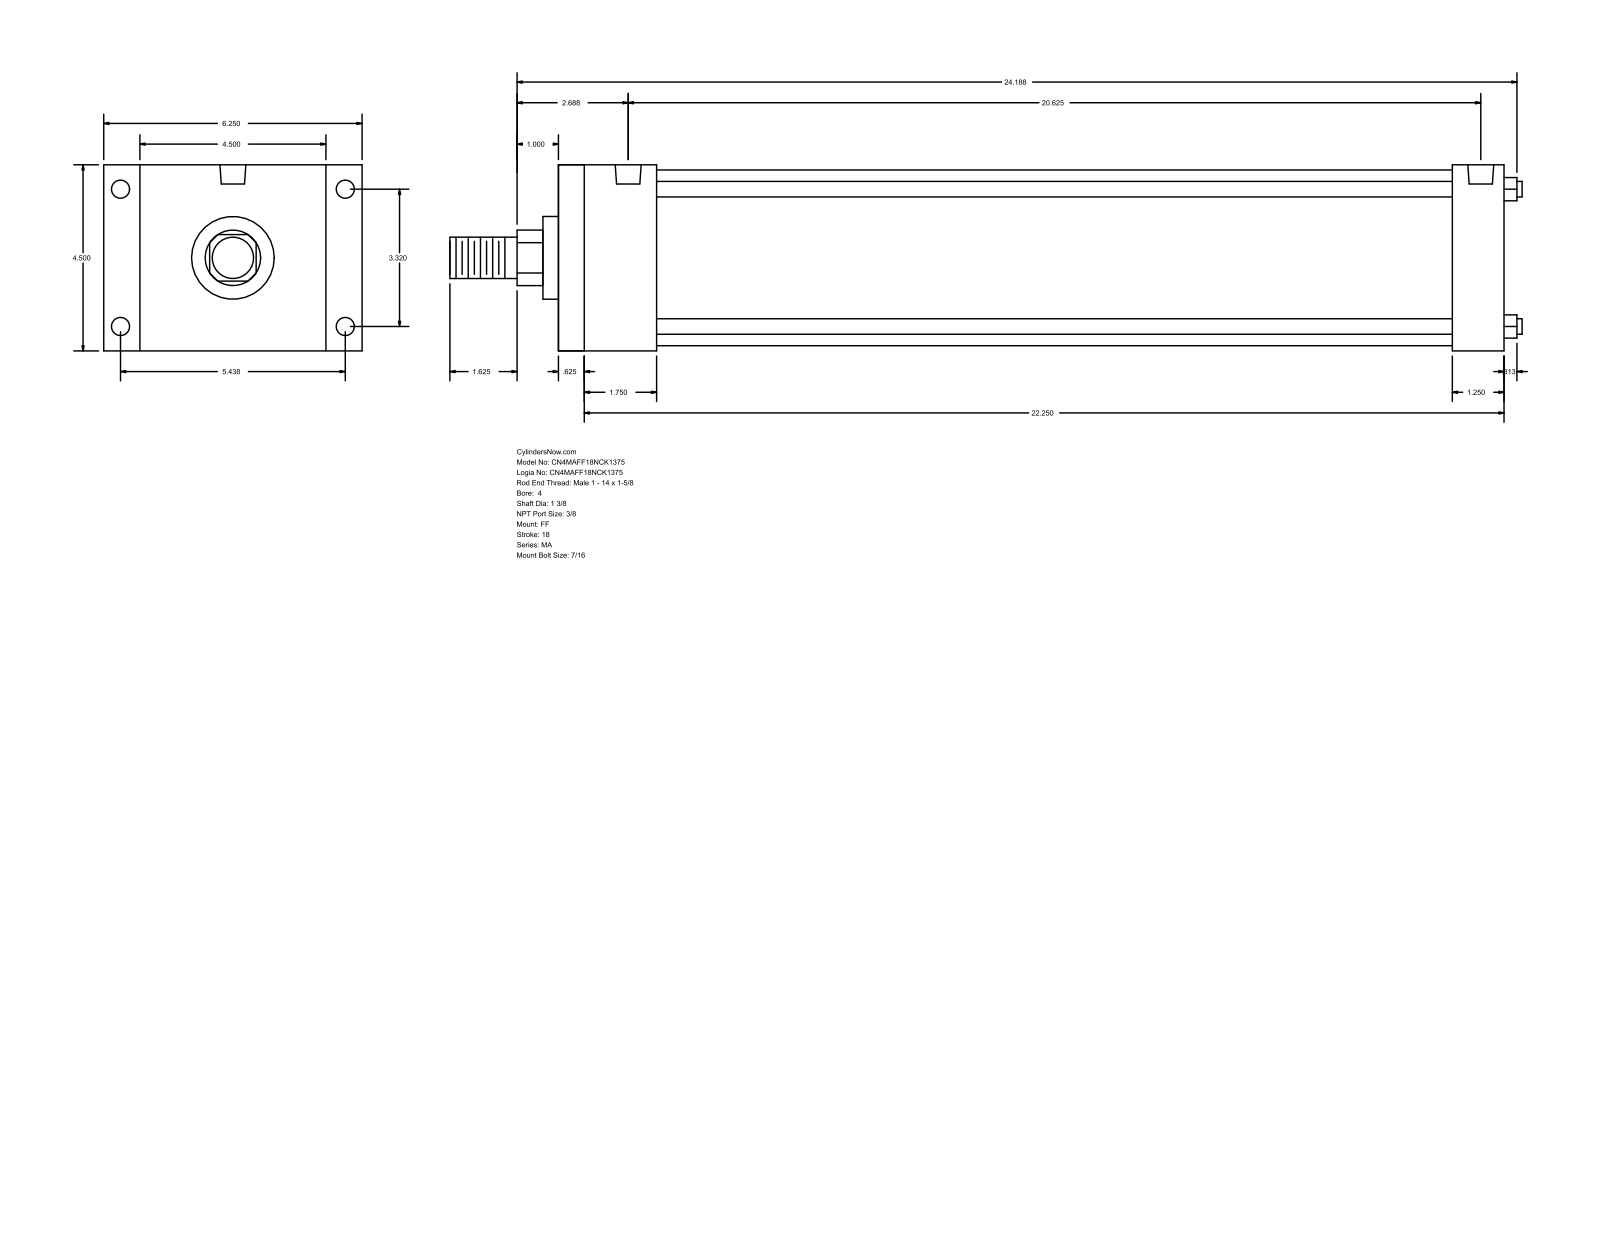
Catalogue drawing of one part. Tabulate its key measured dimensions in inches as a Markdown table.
| quantity | value |
| --- | --- |
| part name | MA_FF__0400_1.375 |
| STEP written by | GSSL Pune (CONFIG_CONTROL_DESIGN) |
| units | inches |
| bodies | 0 solids, 92 faces (64 planar, 28 cylindrical, 0 other) |
| overall size | 25.937 × 6.25 × 4.5 |
| round holes (diameter × count) | 0.437 × 8, 0.627 × 2 |
| round bosses / shafts (diameter × count) | 0.375 × 4, 4.25 × 1, 2 × 1, 1.375 × 1, 1 × 1 |
| partial cylindrical surfaces (radius × count) | 0.672 × 1 |
| main face-to-face distances | 4.5, 22.875, 0.625, 22.25, 0.875, 5.375, 21.625, 21, 1.25, 2.375 |
| hole center spacings | 3.32, 5.438, 6.371, 20.25, 0.187, 0.188, 20.437, 20.438 |
